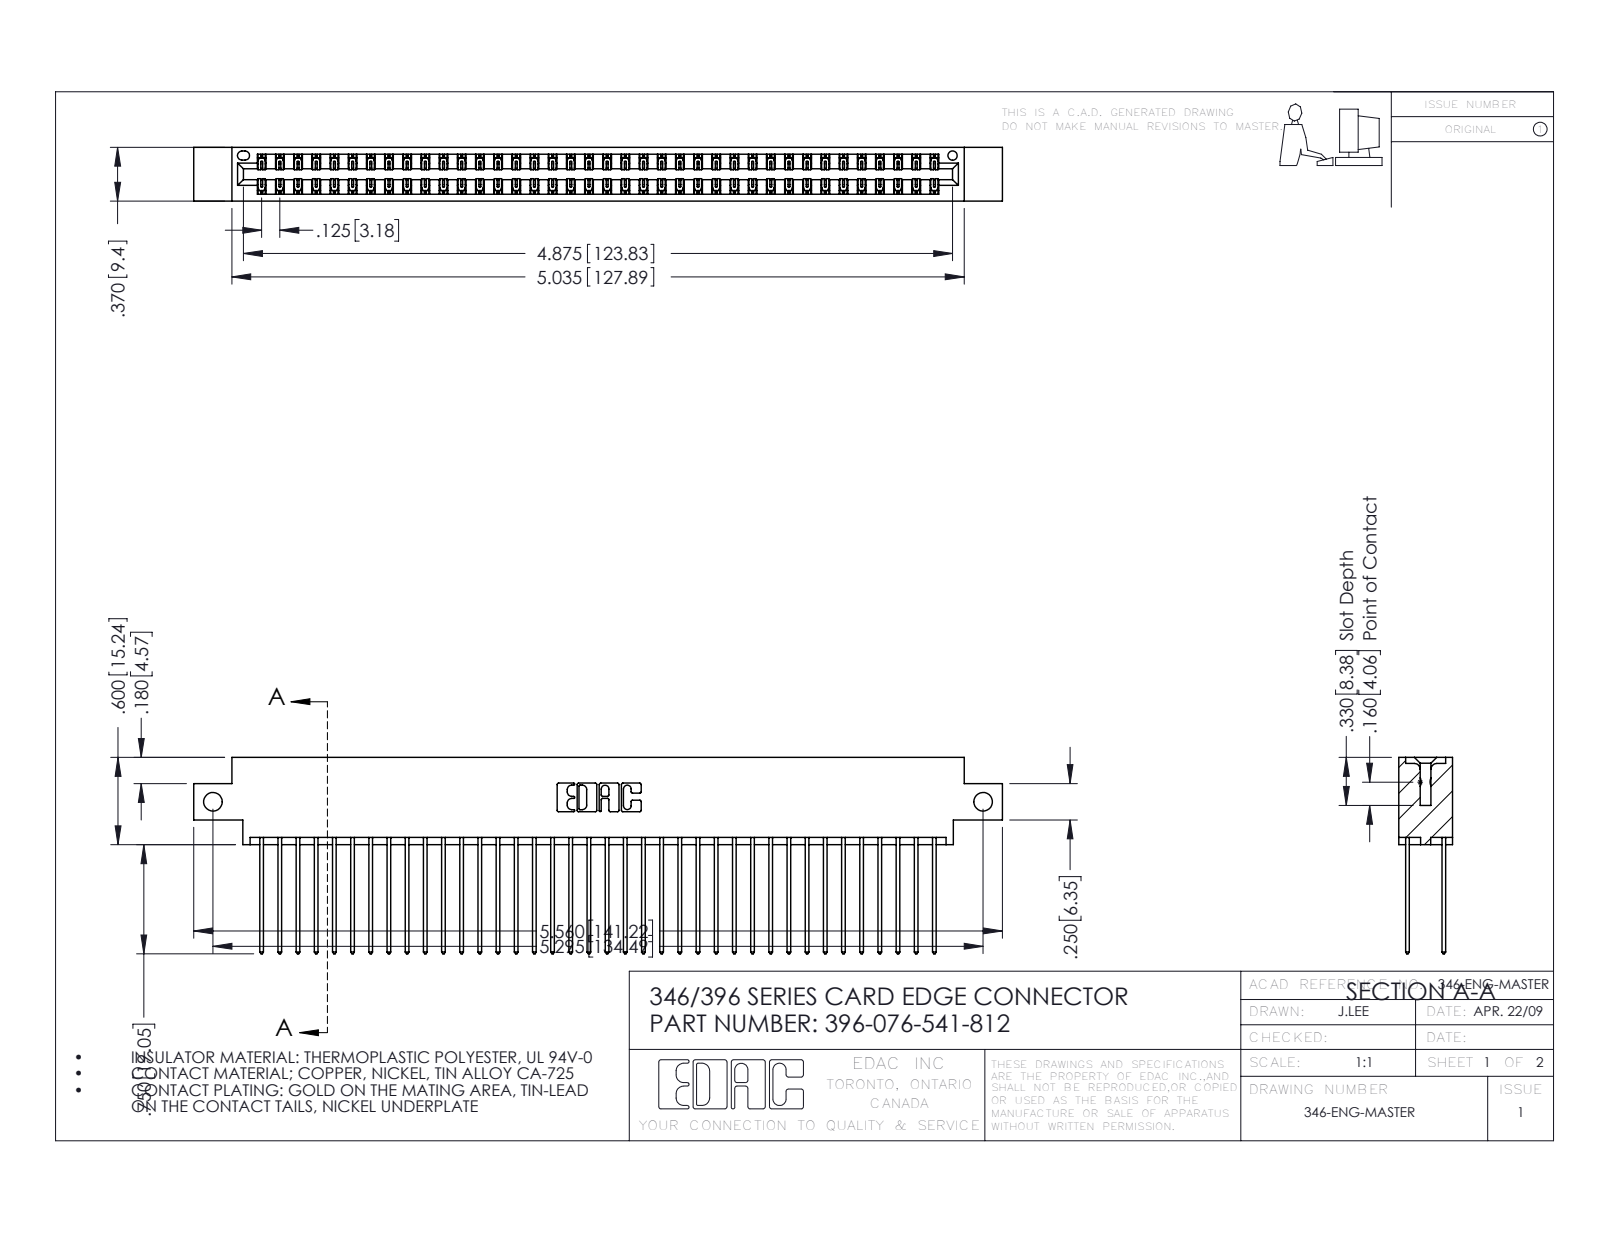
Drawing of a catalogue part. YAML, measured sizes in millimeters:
part_name: "396-076-541-812; 346 Part_0.170 Offset - Side Mount; 345-292-001_345-293-141"
step_written_by: "SolidWorks 2016 (CONFIG_CONTROL_DESIGN)"
units: millimeters
bodies: {solids: 77, faces: 4078, planar: 2740, cylindrical: 1338, other: 0}
overall_size: [141.2, 34.3, 9.4]
volume: 13900
surface_area: 21230
round_holes:
  - {diameter: 3.3, count: 2}
  - {diameter: 1.6, count: 1}
partial_cylinders:
  - {radius: 0.2, count: 114}
  - {radius: 0.3, count: 76}
  - {radius: 0.3, count: 22}
  - {radius: 0.2, count: 6}
  - {radius: 0.8, count: 6}
  - {radius: 0.7, count: 3}
  - {radius: 0.4, count: 2}
  - {radius: 0.6, count: 2}
face_to_face_distances: [1.2, 8.2, 6.4, 1.8, 7.6, 0.6, 9.4, 7, 5.7, 3.8]
hole_center_spacings: [134.5]
